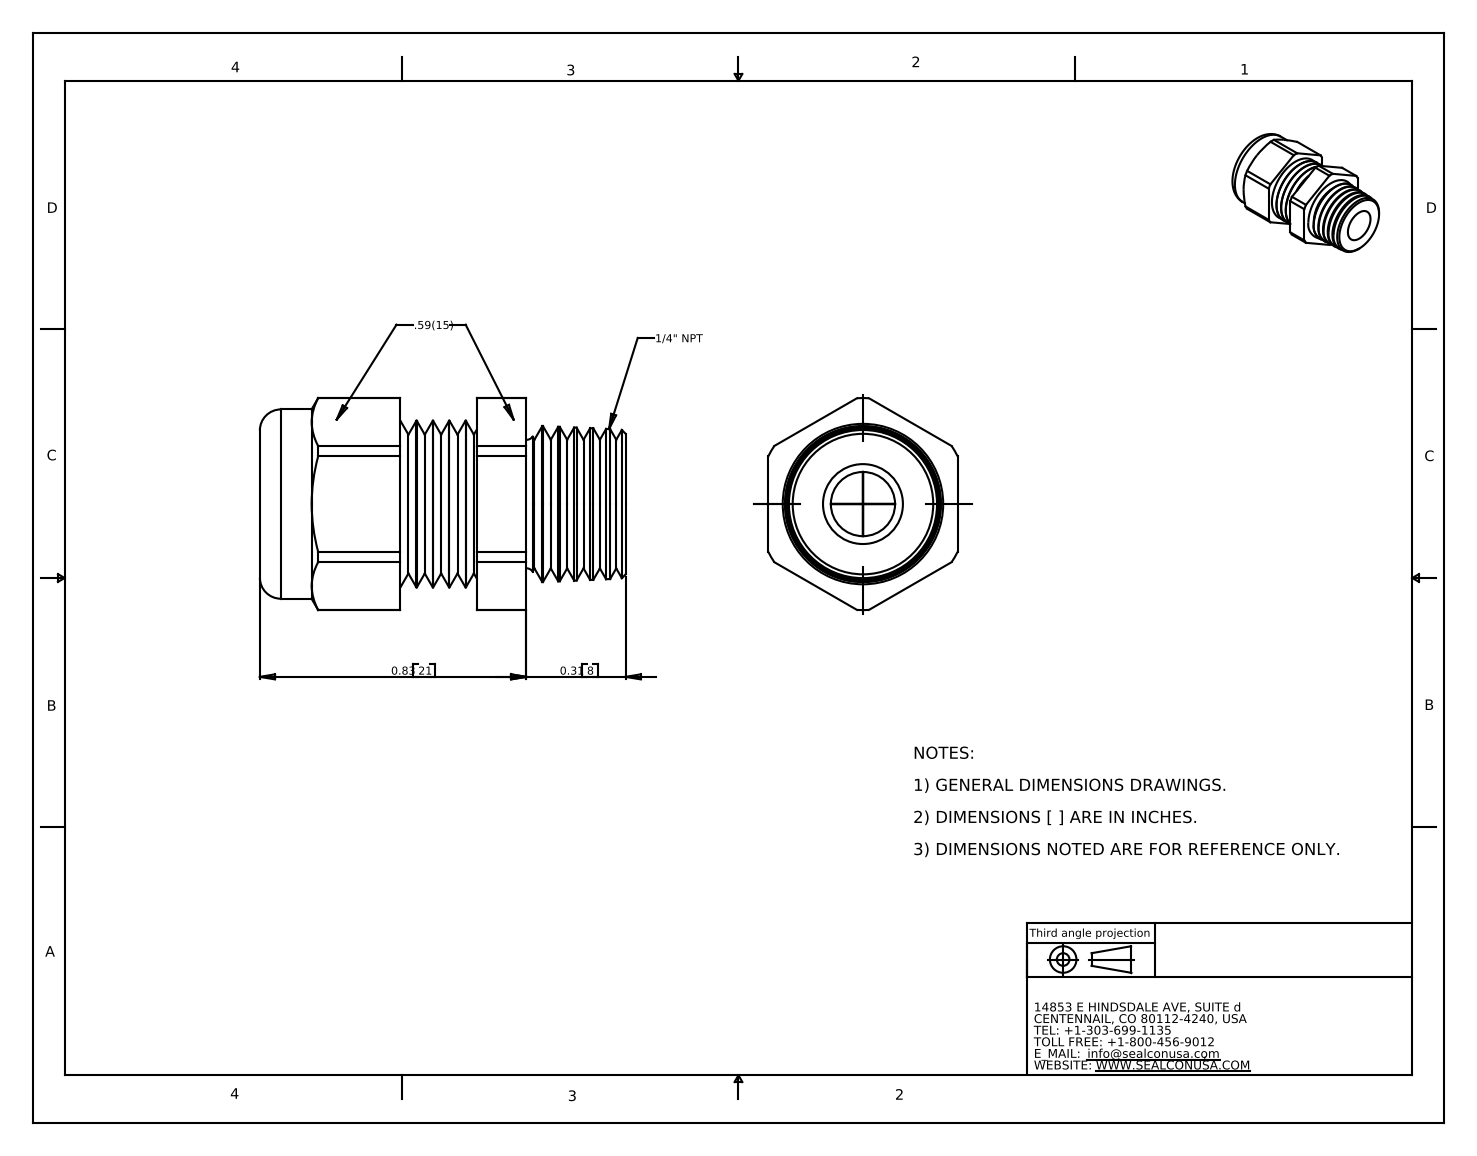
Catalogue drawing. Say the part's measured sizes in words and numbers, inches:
The part is named "CD07AR-BK". Its 3-D file was written by "SolidWorks 2007 (CONFIG_CONTROL_DESIGN)". It is 2 solids with 124 faces: 20 planar, 32 cylindrical and 72 other. Overall it measures 1.14 by 0.661 by 0.59 inches. Its volume is 0.216 cubic inches and its surface area 4.771 square inches. Round holes: 1 of diameter 0.2, 1 of diameter 0.417. Round bosses or shafts: 1 of diameter 0.59, 1 of diameter 0.519. Partial cylindrical surfaces (rounded edges, fillets, slot ends): 1 of radius 0.33. The main face-to-face distances are 0.59, 0.669, 0.979, 0.31, 0.141, 0.81, 1.12, 0.656, 0.515, 0.154.
